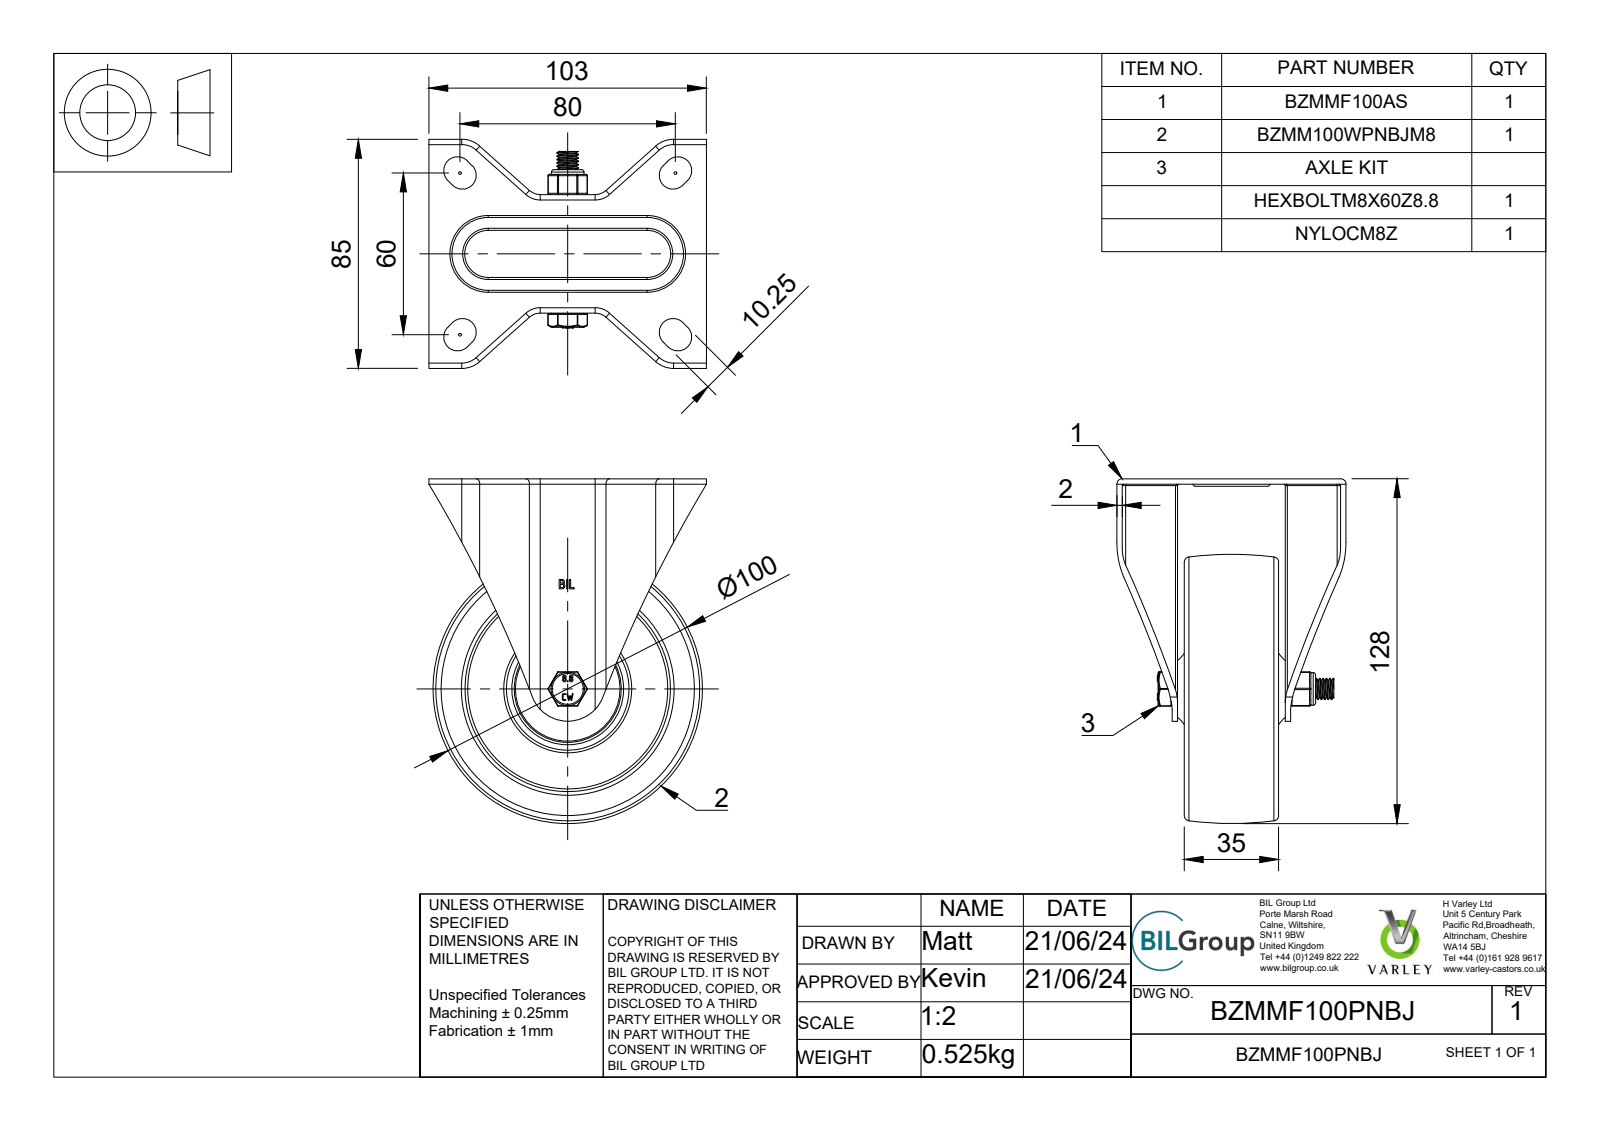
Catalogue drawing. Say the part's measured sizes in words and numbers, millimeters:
The part is named "BZMMF100PNBJ v3; BZMMF100AS v1; BZMMF100AS; ZINC PLATED, PRESSED STEEL BRACKET (+7 more)". Its 3-D file was written by "Autodesk Translation Framework v13.14.0.145 (AUTOMOTIVE_DESIGN)". It is 21 solids with 825 faces: 318 planar, 224 cylindrical and 283 other. Overall it measures 128 by 103 by 85 millimeters. Its volume is 198 903 cubic millimeters and its surface area 122 167 square millimeters. Round holes: 2 of diameter 0.66, 1 of diameter 8, 1 of diameter 8.25, 1 of diameter 8.4, 1 of diameter 8.6, 1 of diameter 15, 1 of diameter 20, 1 of diameter 22.5, 1 of diameter 26, 1 of diameter 30, 1 of diameter 31, 1 of diameter 32. Round bosses or shafts: 1 of diameter 45.5, 1 of diameter 39.75, 1 of diameter 37, 1 of diameter 30.5, 1 of diameter 23, 1 of diameter 19.75, 1 of diameter 18, 1 of diameter 14.95. Partial cylindrical surfaces (rounded edges, fillets, slot ends): 26 of radius 0.5, 12 of radius 0.25, 8 of radius 0.75, 8 of radius 2, 8 of radius 5.12, 4 of radius 0.33, 4 of radius 0.64, 4 of radius 3. The main face-to-face distances are 2, 12, 17, 14.26, 22.5, 19.5, 3, 20, 2.5, 15. The hole center spacings are 4.65, 2.49.
